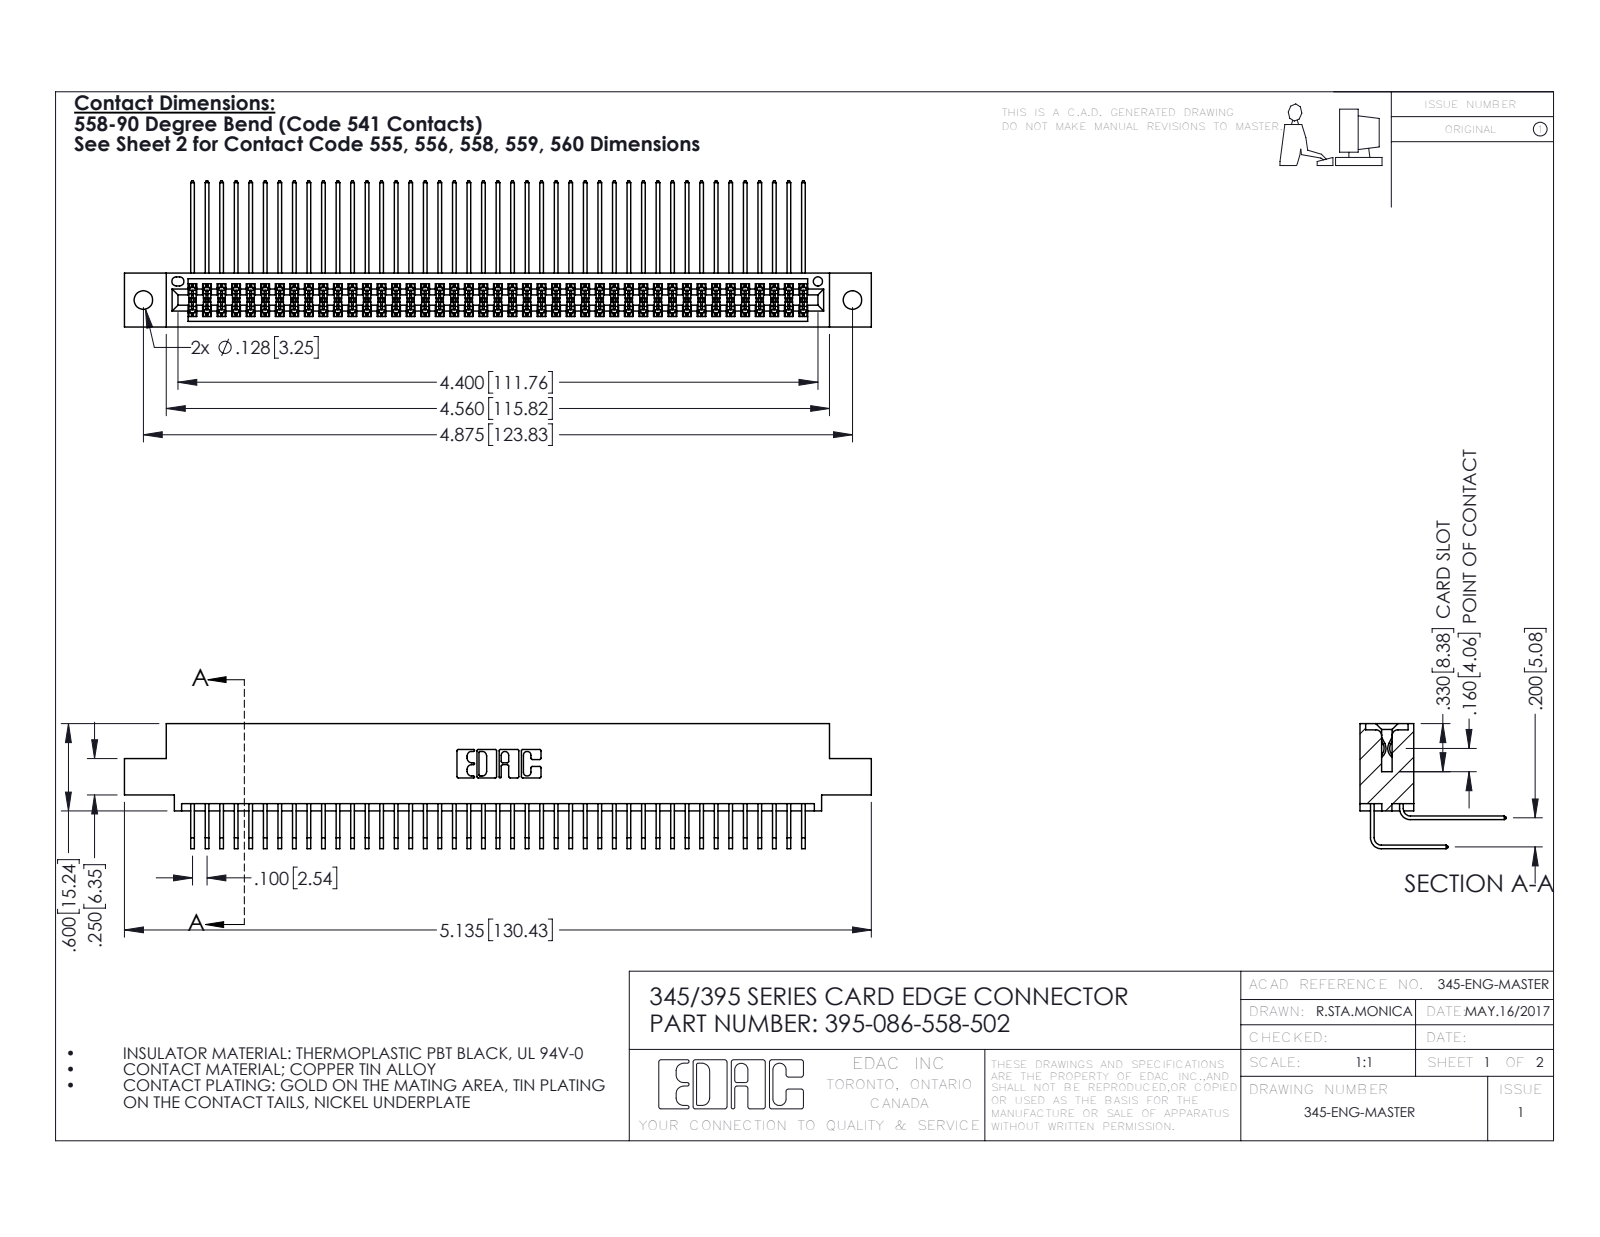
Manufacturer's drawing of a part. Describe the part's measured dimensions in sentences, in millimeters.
The part is named "345 Part_0.110 Offset - 0.128 Dia; 395-086-558-502; 345-292-001_558 Tail - 2; 345-292-001_558 559 Tail - 1". Its 3-D file was written by "SolidWorks 2016 (CONFIG_CONTROL_DESIGN)". It is 87 solids with 4602 faces: 3094 planar, 1508 cylindrical and 0 other. Overall it measures 130.4 by 25.5 by 21.8 millimeters. Its volume is 13 100 cubic millimeters and its surface area 21 480 square millimeters. Round holes: 2 of diameter 3.3, 1 of diameter 1.6. Partial cylindrical surfaces (rounded edges, fillets, slot ends): 130 of radius 0.2, 22 of radius 0.3, 6 of radius 0.2, 6 of radius 0.8, 3 of radius 0.7, 2 of radius 0.4, 2 of radius 0.5, 2 of radius 0.6. The main face-to-face distances are 1.8, 7.6, 5.1, 9.4, 2.5, 6.9, 0.6, 5.7, 0.6, 4.4. The hole center spacings are 6.9, 117.8, 123.8.
